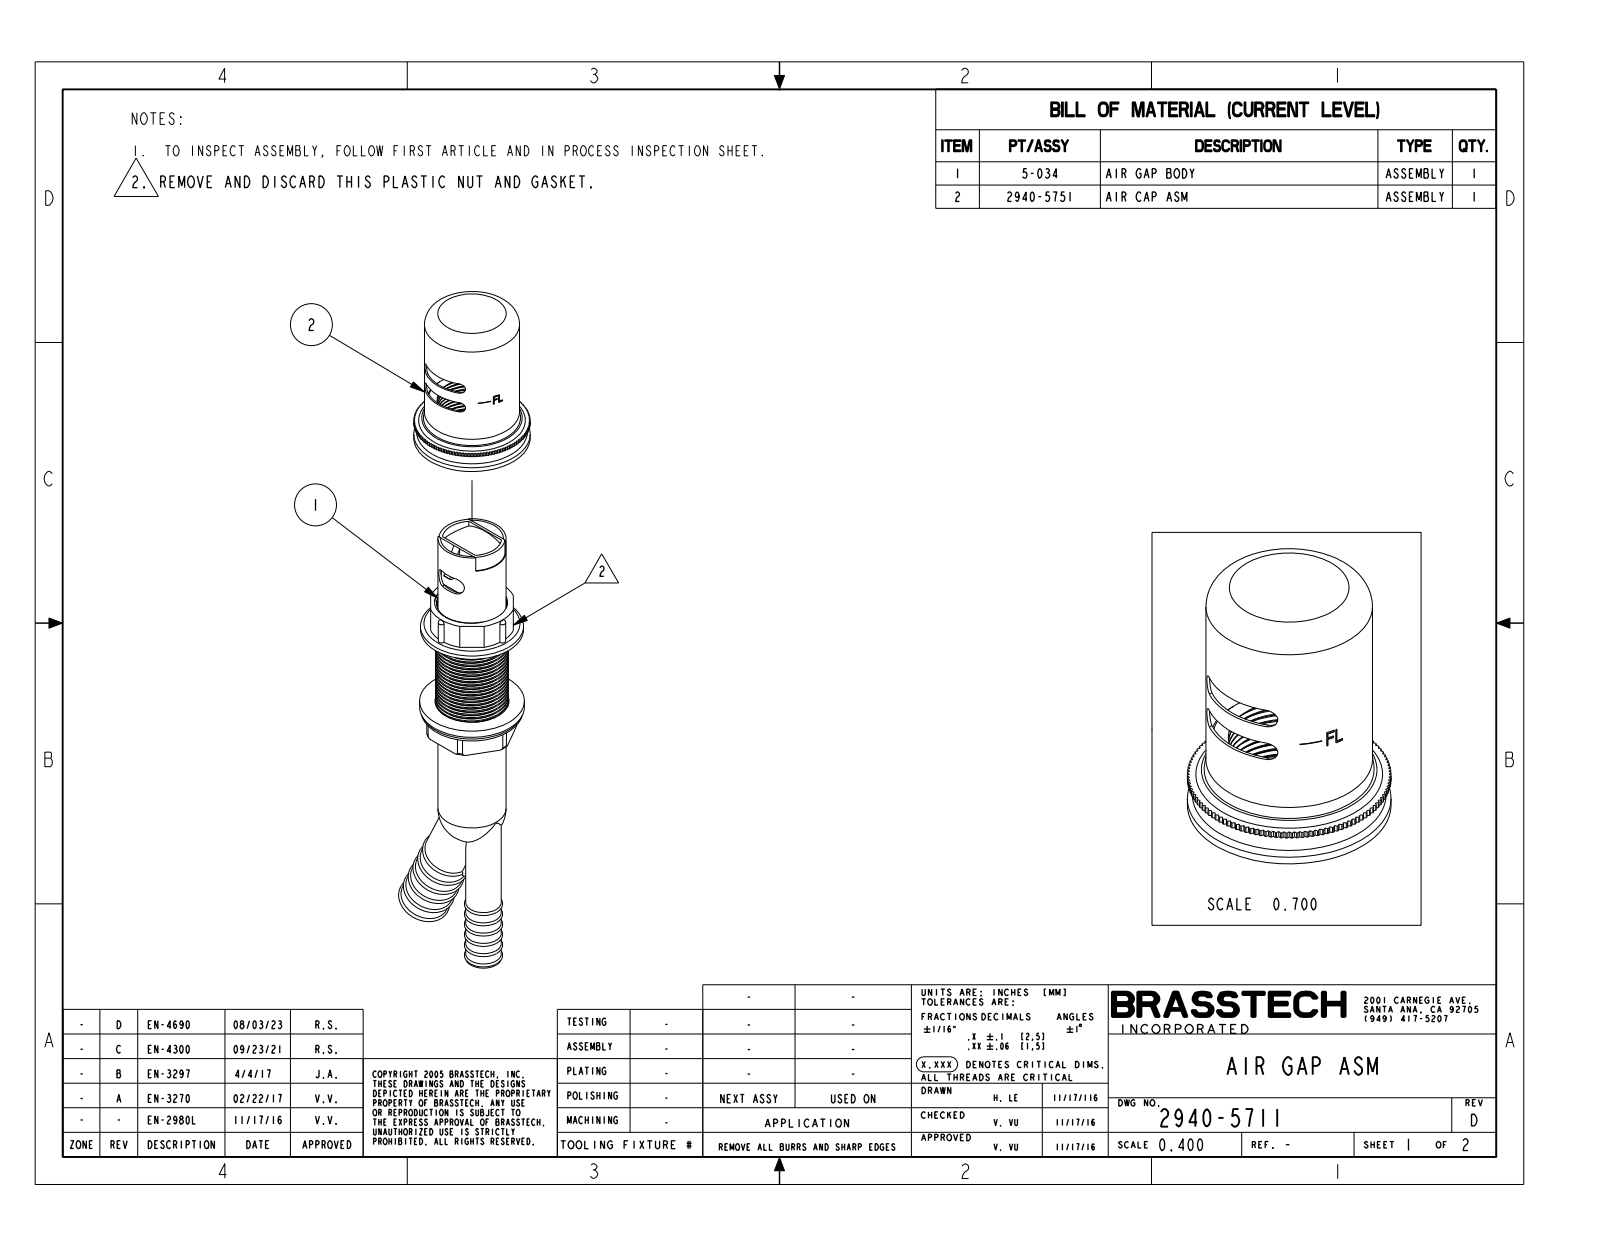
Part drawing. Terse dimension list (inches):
name: 2940-5711_2
written by: CREO PARAMETRIC BY PTC INC, 2018400 (AUTOMOTIVE_DESIGN)
unit: in
bodies: 1 solid, 643 faces (312 planar, 256 cylindrical, 75 other)
size: 8.803 × 2.582 × 2
volume: 10.06 in³; area: 80.67 in²
holes: 1× ⌀1.2, 1× ⌀1.27, 1× ⌀1.28, 1× ⌀1.575, 1× ⌀1.865
bosses: 1× ⌀2, 1× ⌀1.904, 1× ⌀1.8, 1× ⌀1.76, 1× ⌀1.669, 1× ⌀1.635, 1× ⌀1.625, 1× ⌀1.259
rounds: 6× R0.04, 4× R0.098, 2× R0.157, 1× R0.808
face distances: 0.92, 3.505, 3.535, 2.585, 2.615, 0.03, 1.352, 0.432, 2.153, 2.183
